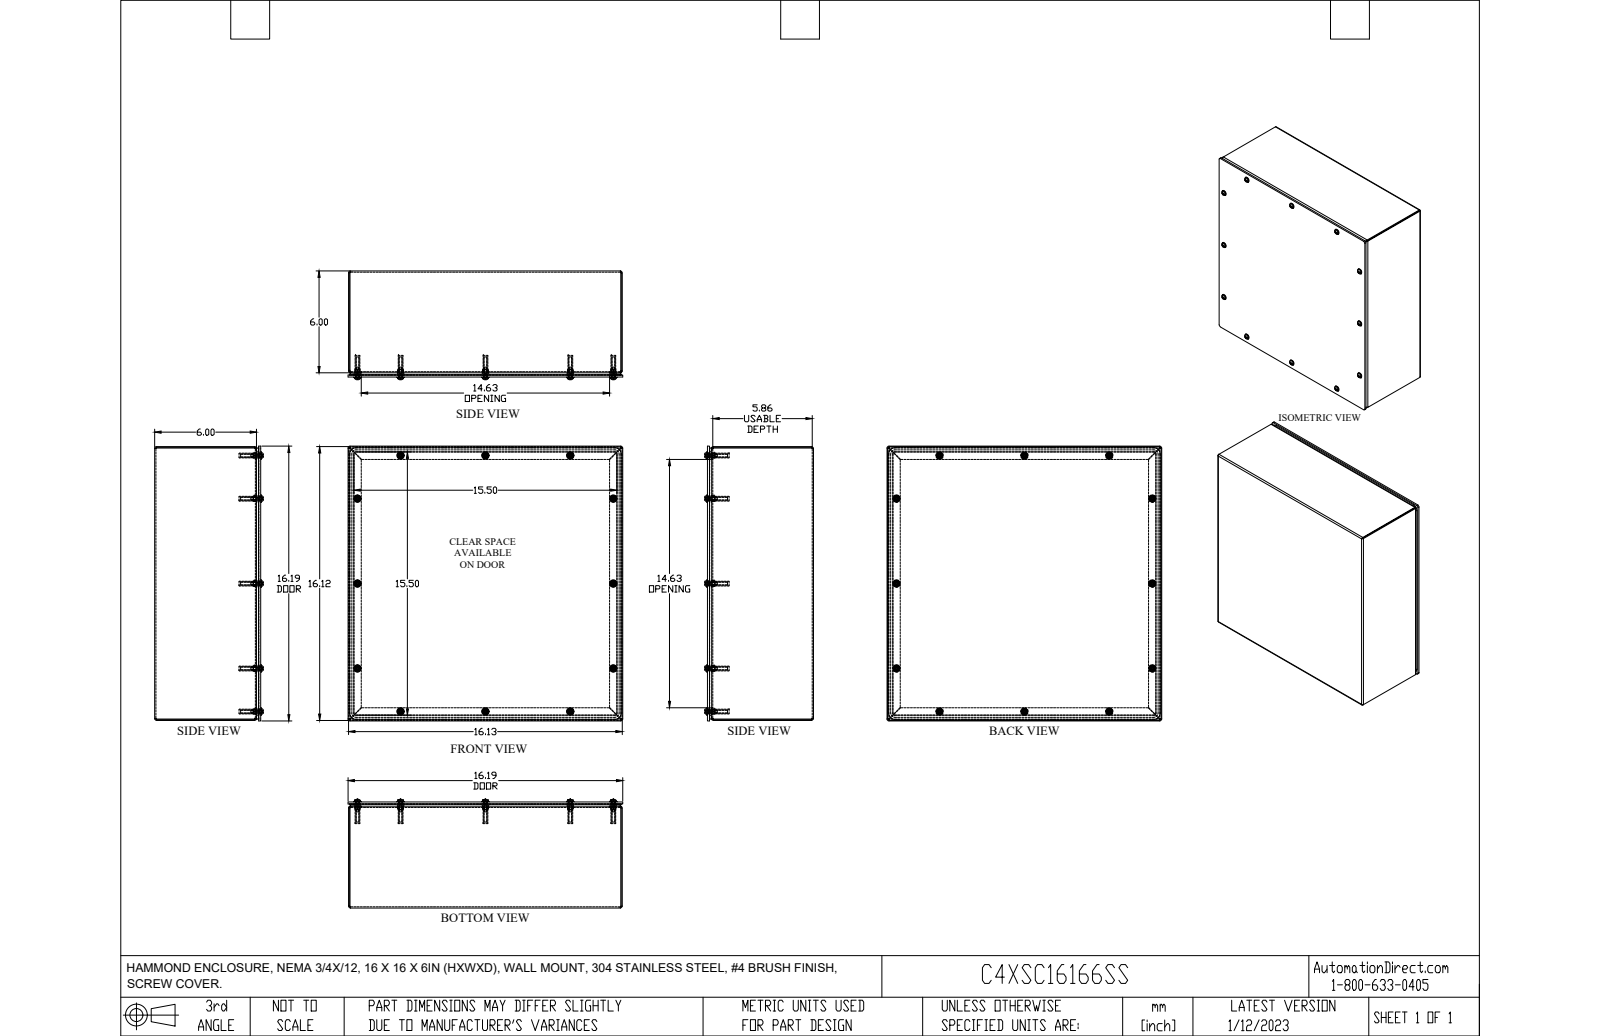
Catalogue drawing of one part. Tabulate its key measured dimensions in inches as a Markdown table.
| quantity | value |
| --- | --- |
| part name | C3SC16166GY |
| STEP written by | SolidWorks 2021 (AUTOMOTIVE_DESIGN) |
| units | inches |
| bodies | 40 solids, 1310 faces (842 planar, 228 cylindrical, 240 other) |
| overall size | 16.188 × 16.188 × 6.4 |
| volume | 131.1 in³ |
| surface area | 3 360 in² |
| round holes (diameter × count) | 0.159 × 12, 0.16 × 12, 0.25 × 12 |
| round bosses / shafts (diameter × count) | 0.44 × 12, 0.39 × 12, 0.24 × 12, 0.19 × 12, 0.148 × 12, 0.275 × 10, 0.275 × 2 |
| partial cylindrical surfaces (radius × count) | 0.16 × 12, 0.036 × 8, 0.04 × 8, 0.108 × 8, 0.11 × 8, 0.125 × 8, 0.126 × 4, 0.374 × 4 |
| main face-to-face distances | 0.072, 0.07, 16.053, 0.125, 6.25, 6.125, 6.18, 6.055, 6.178, 6.053 |
| hole center spacings | 5, 7.953, 12.792, 14.629, 15.882, 15.075, 3.589, 10 |
